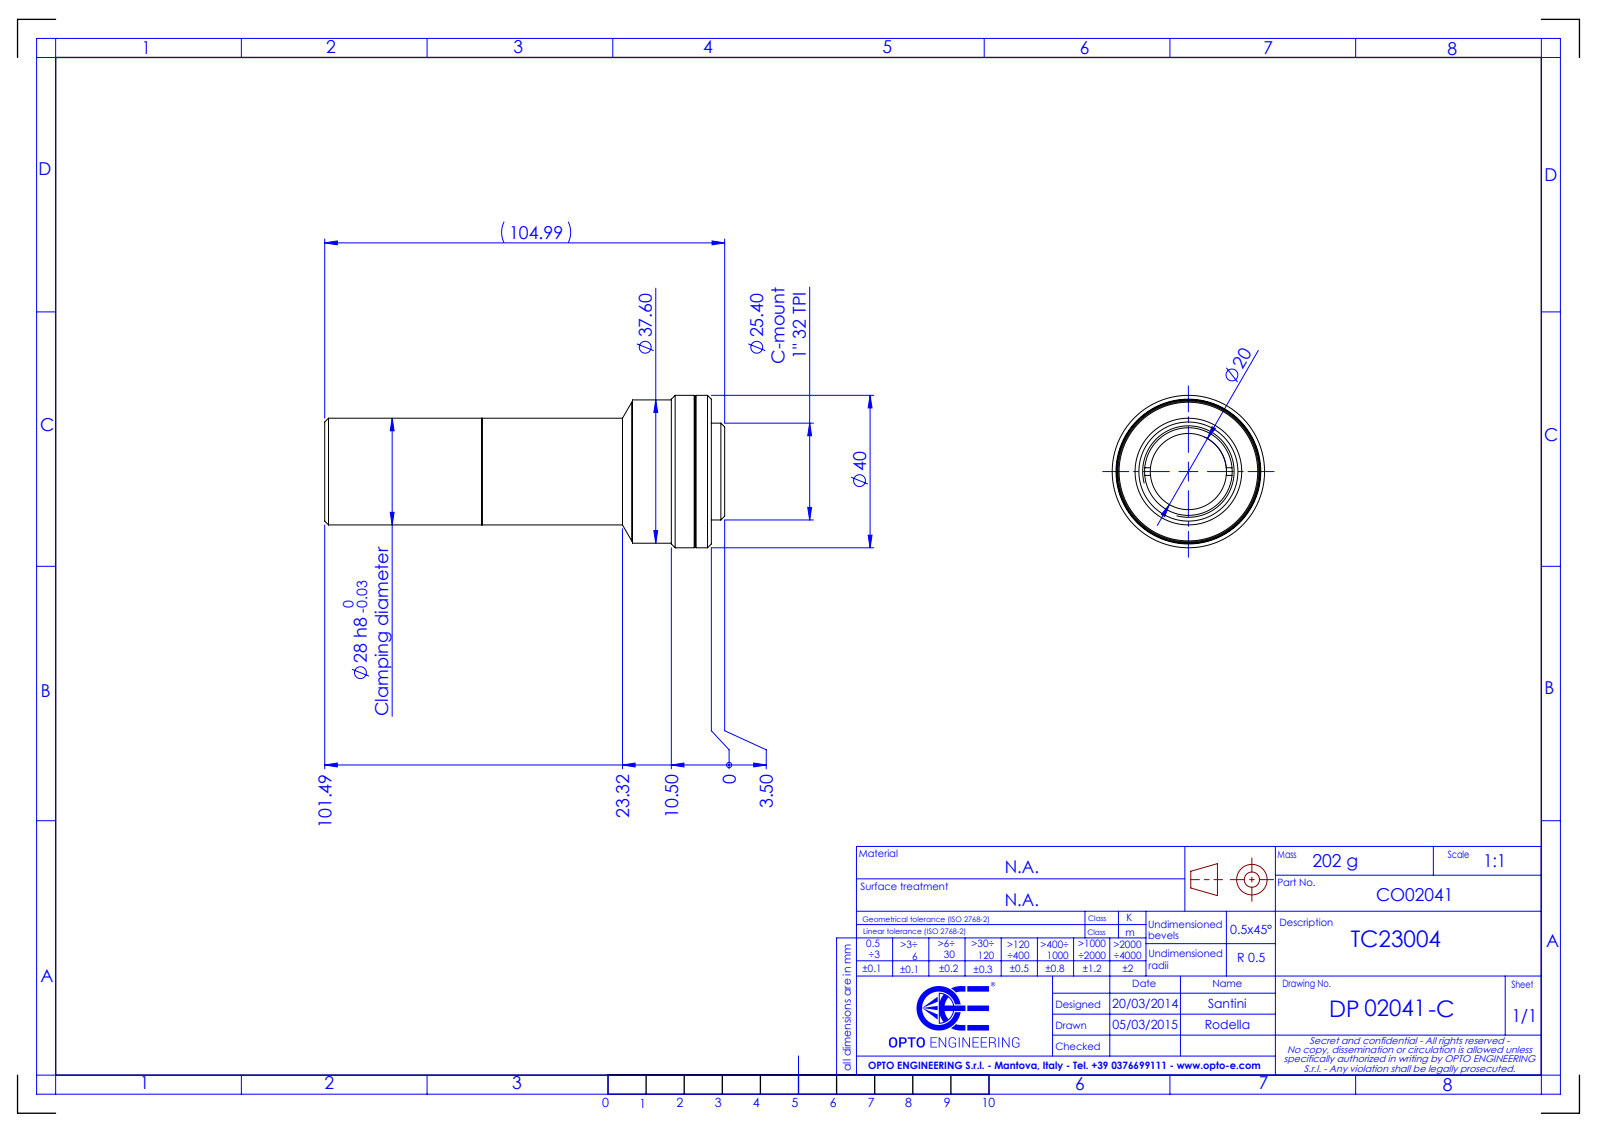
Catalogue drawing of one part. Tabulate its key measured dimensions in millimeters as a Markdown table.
| quantity | value |
| --- | --- |
| part name | DP02041_TC23004 |
| STEP written by | SolidWorks 2021 (CONFIG_CONTROL_DESIGN) |
| units | millimeters |
| bodies | 0 solids, 68 faces (24 planar, 28 cylindrical, 16 other) |
| overall size | 104.99 × 40 × 40 |
| round holes (diameter × count) | 20 × 1, 22.3 × 1, 22.5 × 1, 23 × 1, 37.7 × 1 |
| round bosses / shafts (diameter × count) | 40 × 1, 39.8 × 1, 37.6 × 1, 36.4 × 1, 28 × 1, 25.4 × 1 |
| main face-to-face distances | 0.4, 3.5, 7.5, 3, 4.4, 4, 0.5, 4.5, 3.1, 52.71 |
